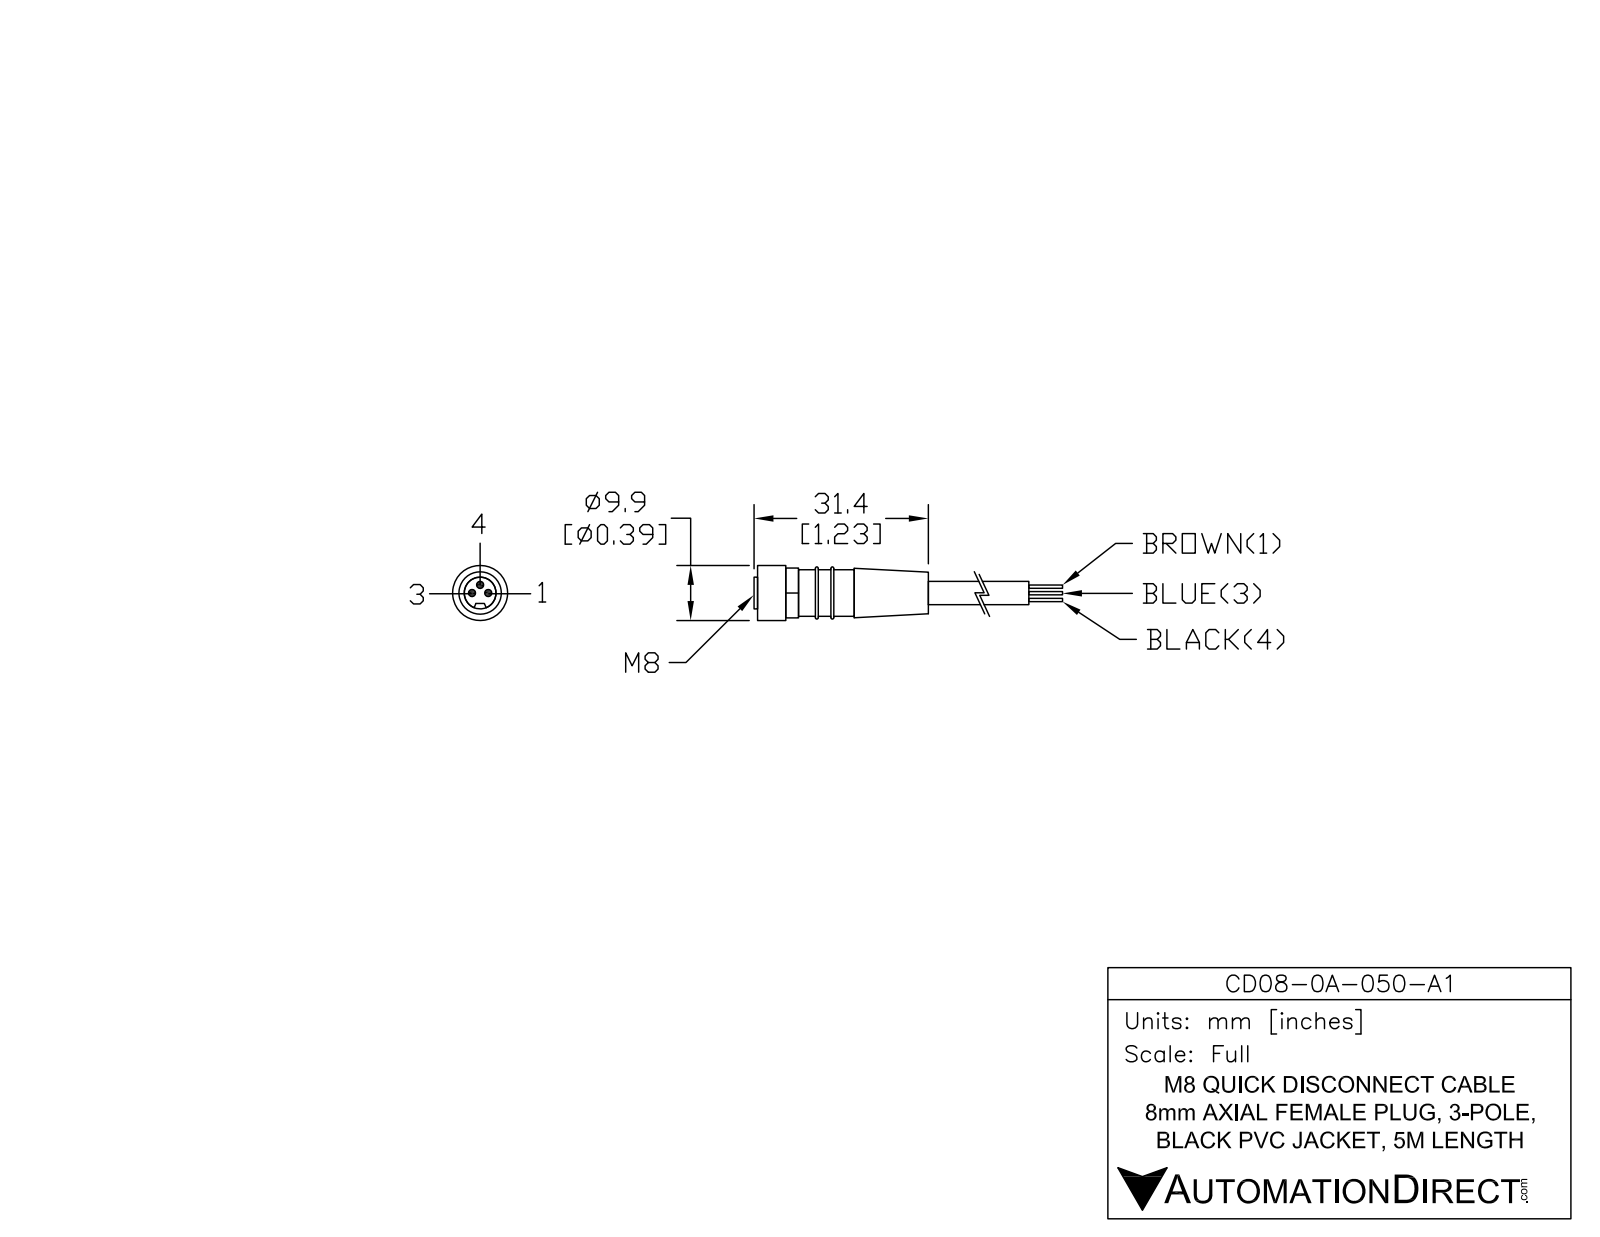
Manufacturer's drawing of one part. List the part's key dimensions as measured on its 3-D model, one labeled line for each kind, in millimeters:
Part name (STEP PRODUCT): CD08-0A-050-A1
STEP written by: SolidWorks 2017 (AUTOMOTIVE_DESIGN)
Units: millimetres
Bodies: 4 solids, 304 faces (222 planar, 78 cylindrical, 4 other)
Overall size (bounding box): 134.6 × 10 × 10
Volume: 4 158 mm³ · Surface area: 3 249 mm²
Round holes (diameter × count): ⌀0.9 ×3, ⌀5.6 ×1, ⌀8 ×1
Round bosses / shafts (diameter × count): ⌀10 ×1, ⌀5.5 ×1, ⌀4.8 ×1
Partial cylindrical surfaces — rounded edges, fillets, slot ends (radius × count): R0.5 ×1, R4.9 ×1
Main face-to-face distances: 26.9, 9, 0.6, 4.6, 30, 3.1, 4, 34, 7.1, 34.6
Hole centre spacings: 1.6, 2.26, 3.2
